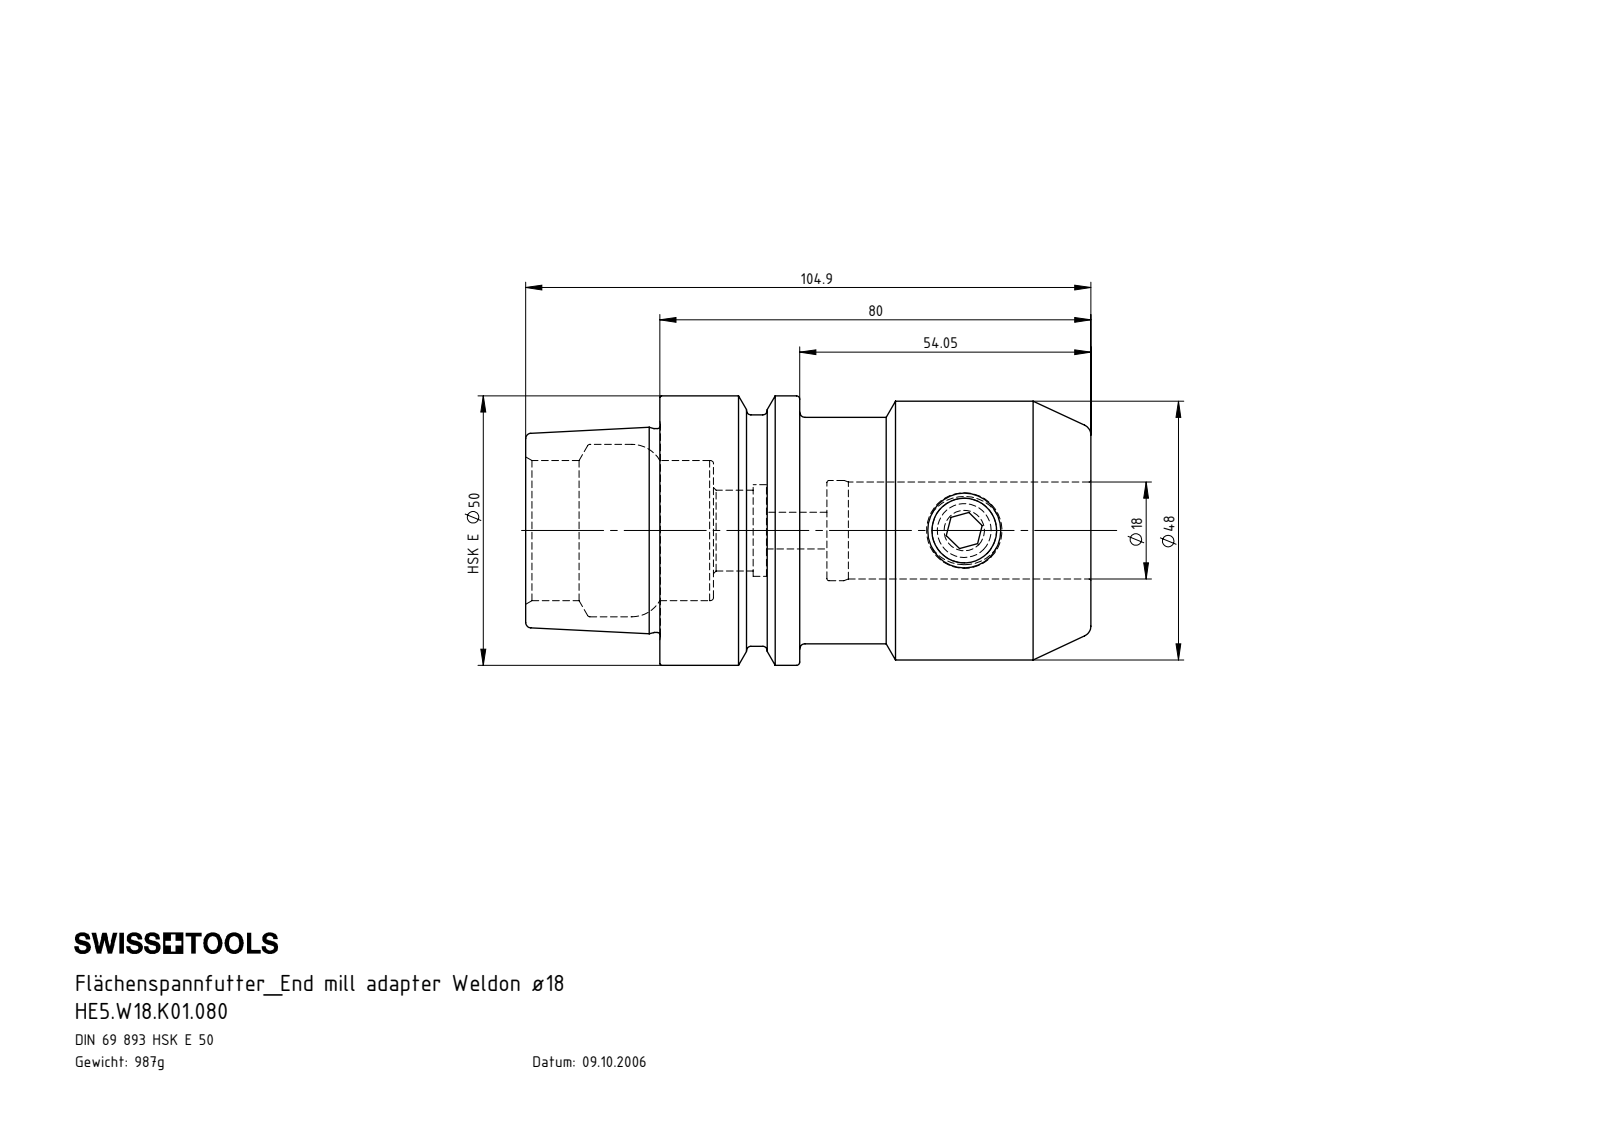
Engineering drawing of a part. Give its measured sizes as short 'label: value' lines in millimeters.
name: HE5-W18.K01.080_B_Fertigbearbeitung; W16-ER1.001.016; HE5.W18.K01.080
written by: SolidWorks 2017 (AUTOMOTIVE_DESIGN)
unit: mm
bodies: 2 solids, 113 faces (19 planar, 32 cylindrical, 62 other)
size: 104.9 × 50 × 50
volume: 125 726 mm³; area: 27 206 mm²
holes: 1× ⌀6.8, 1× ⌀12, 1× ⌀15, 1× ⌀17, 1× ⌀18, 1× ⌀18.6, 1× ⌀26, 1× ⌀32
bosses: 1× ⌀50, 1× ⌀48, 1× ⌀42.95, 1× ⌀42, 1× ⌀37.81, 1× ⌀14
face distances: 80, 25.95, 54.05, 24.9, 50.85, 104.9, 34.85, 9.95, 16, 70.05
